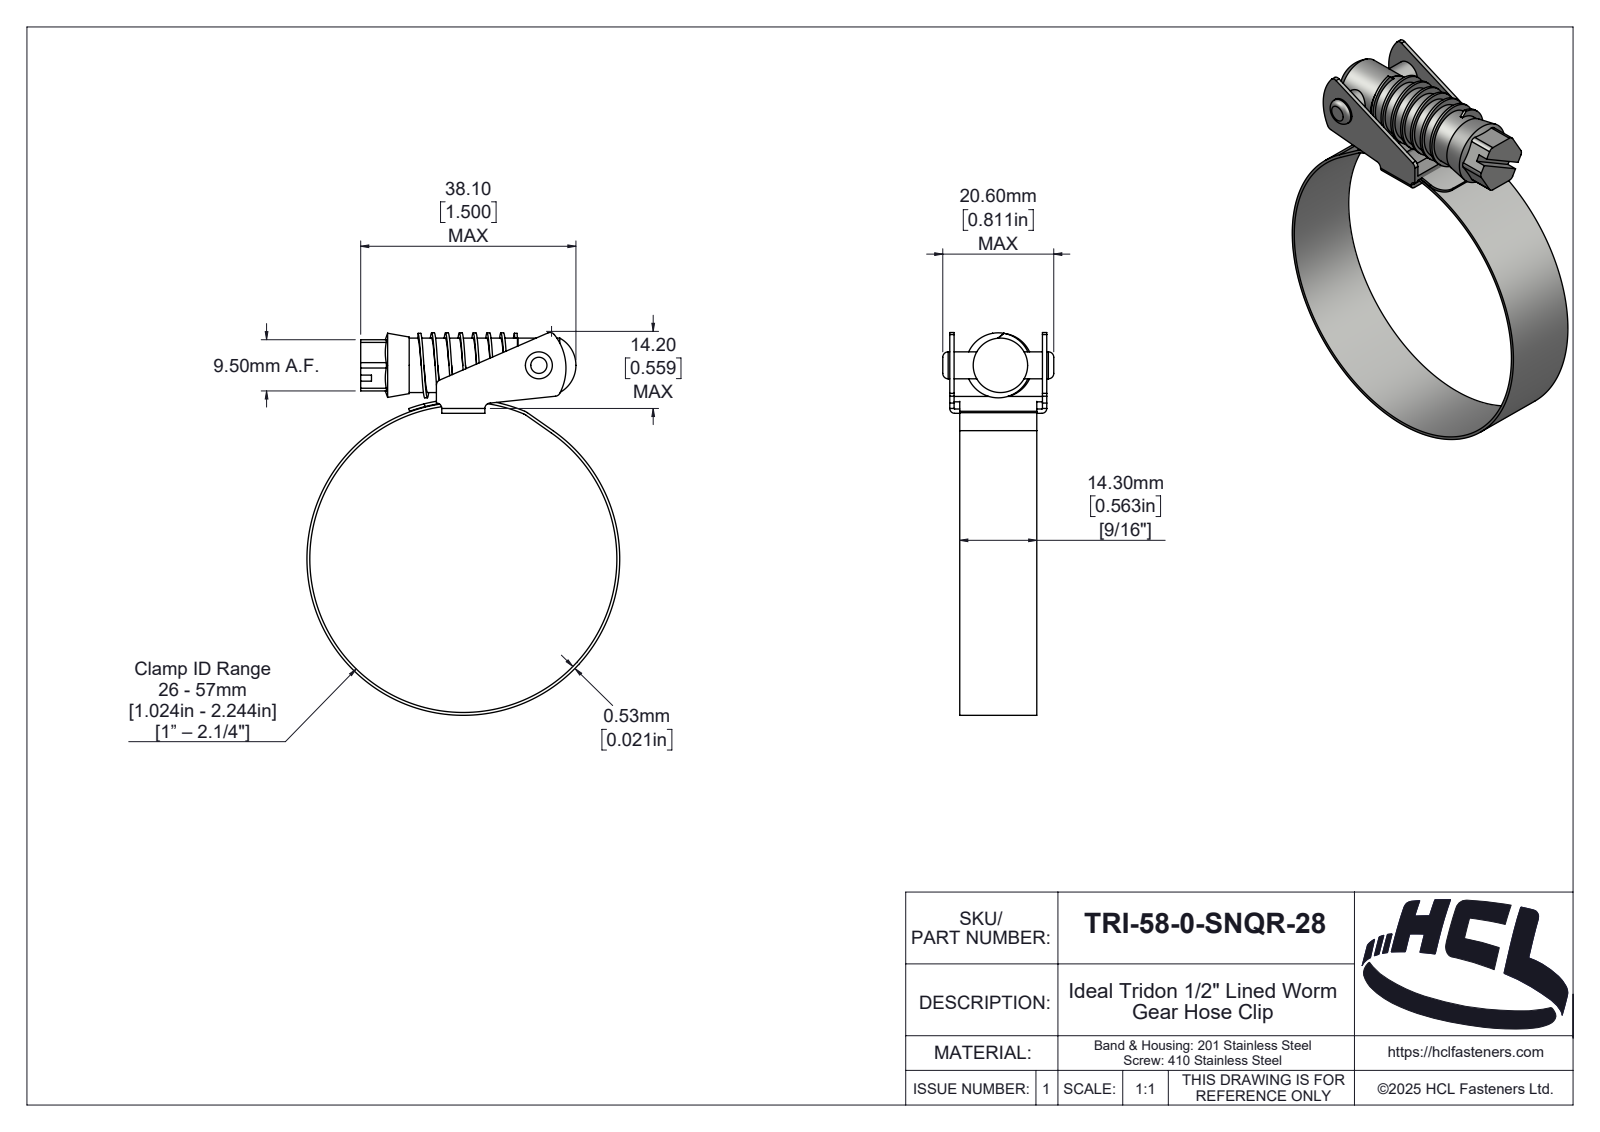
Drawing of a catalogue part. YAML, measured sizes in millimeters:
part_name: "TRI-58-0-SNQR-28"
step_written_by: "SolidWorks 2025 (AUTOMOTIVE_DESIGN)"
units: millimeters
bodies: {solids: 5, faces: 222, planar: 44, cylindrical: 112, other: 66}
overall_size: [71.02, 58.06, 20.6]
volume: 5270
surface_area: 9623
round_holes:
  - {diameter: 5, count: 1}
  - {diameter: 57, count: 1}
round_bosses_or_shafts:
  - {diameter: 58.06, count: 1}
  - {diameter: 10.1, count: 1}
partial_cylinders:
  - {radius: 1, count: 11}
  - {radius: 0.1, count: 2}
  - {radius: 0.9, count: 2}
  - {radius: 3, count: 2}
  - {radius: 0.46, count: 1}
  - {radius: 1.89, count: 1}
  - {radius: 2, count: 1}
  - {radius: 2.35, count: 1}
face_to_face_distances: [0.8, 17.2, 1.85, 16.15, 1.05, 15.35, 18, 16.4, 1, 14.3]
hole_center_spacings: [38.54]
